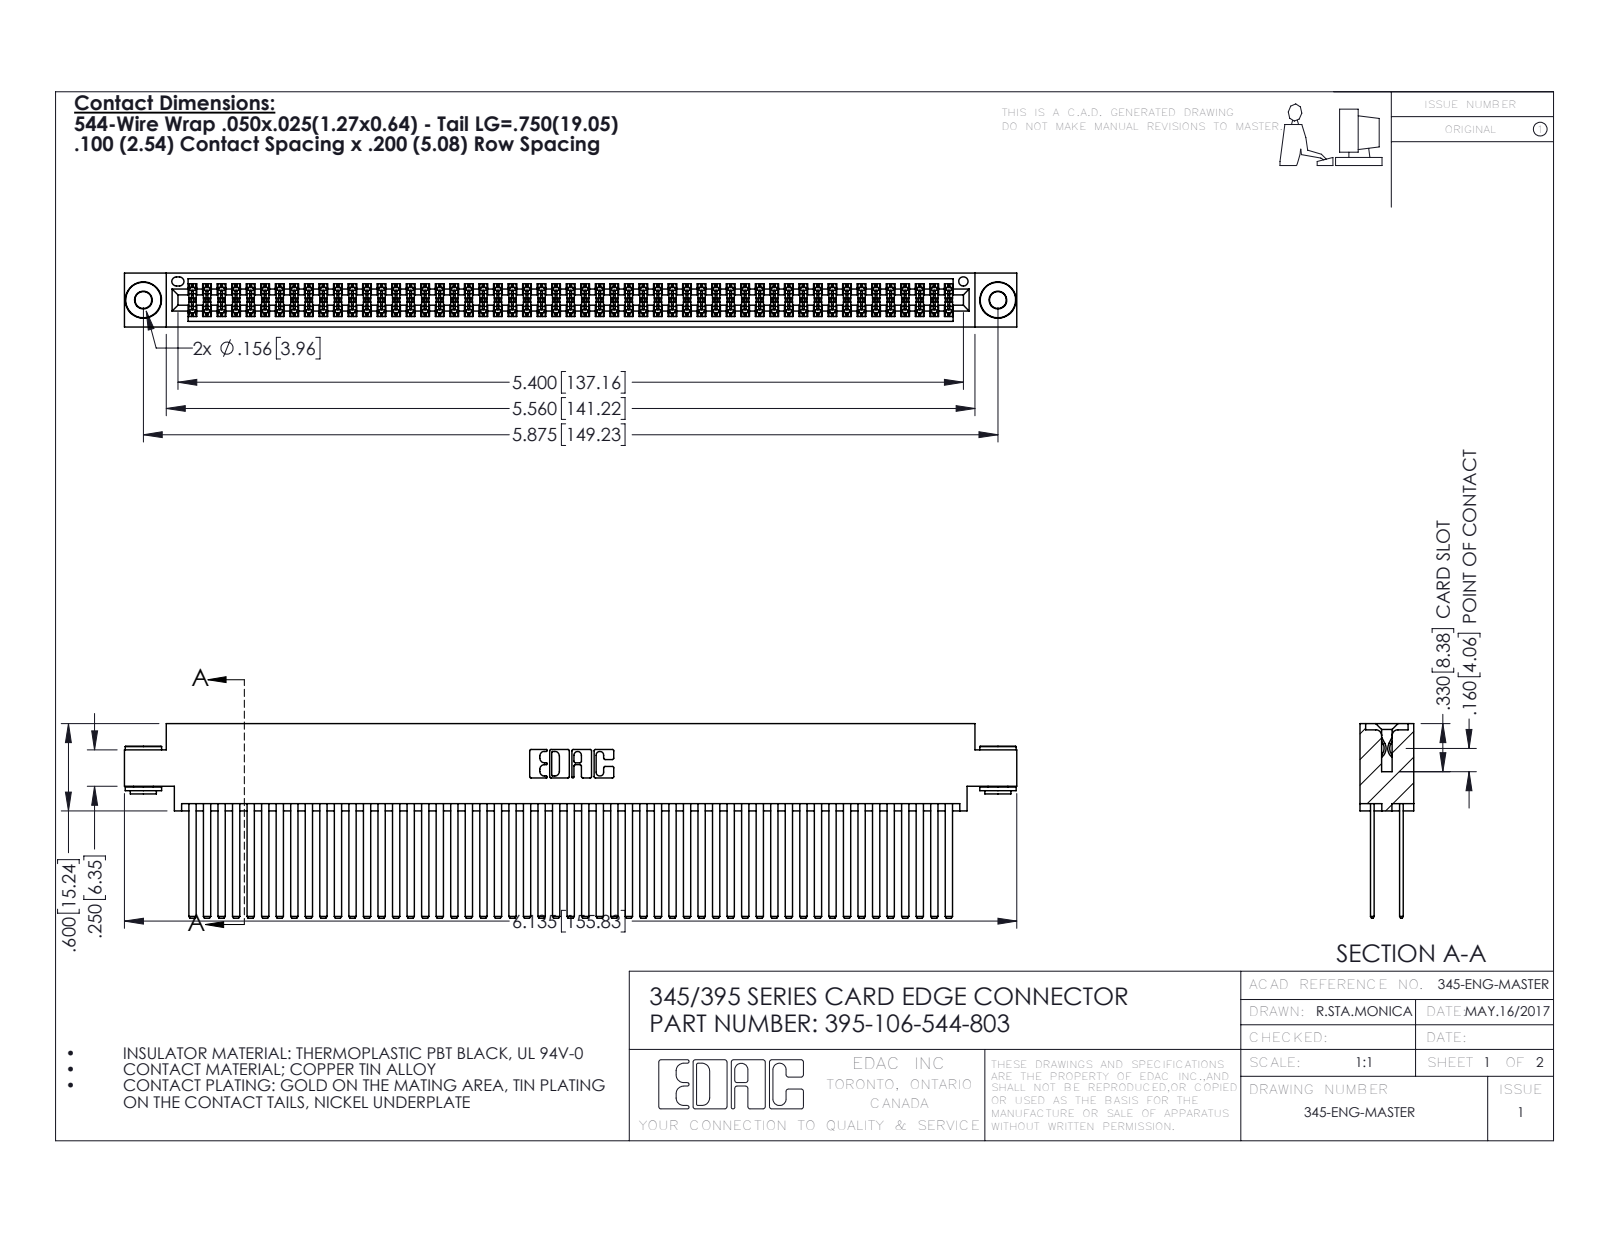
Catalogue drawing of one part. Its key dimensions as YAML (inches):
part_name: "395-106-544-803; 345-250-002_345-250-002-102; 345-292-001_345-293-144; 345 Part_0.170 Offset - 0.156 Dia-TH"
step_written_by: "SolidWorks 2016 (CONFIG_CONTROL_DESIGN)"
units: inches
bodies: {solids: 109, faces: 4832, planar: 3168, cylindrical: 1656, other: 8}
overall_size: [6.135, 1.337, 0.37]
volume: 1.015
surface_area: 45.73
round_holes:
  - {diameter: 0.116, count: 2}
  - {diameter: 0.156, count: 2}
  - {diameter: 0.064, count: 1}
round_bosses_or_shafts:
  - {diameter: 0.25, count: 2}
  - {diameter: 0.18, count: 2}
  - {diameter: 0.136, count: 2}
partial_cylinders:
  - {radius: 0.006, count: 159}
  - {radius: 0.01, count: 22}
  - {radius: 0.007, count: 6}
  - {radius: 0.031, count: 6}
  - {radius: 0.026, count: 3}
  - {radius: 0.014, count: 2}
  - {radius: 0.019, count: 2}
  - {radius: 0.022, count: 2}
face_to_face_distances: [0.2, 0.025, 0.072, 0.098, 0.272, 0.298, 0.225, 0.175, 0.37, 0.15]
hole_center_spacings: [0.27, 5.639, 5.875]
